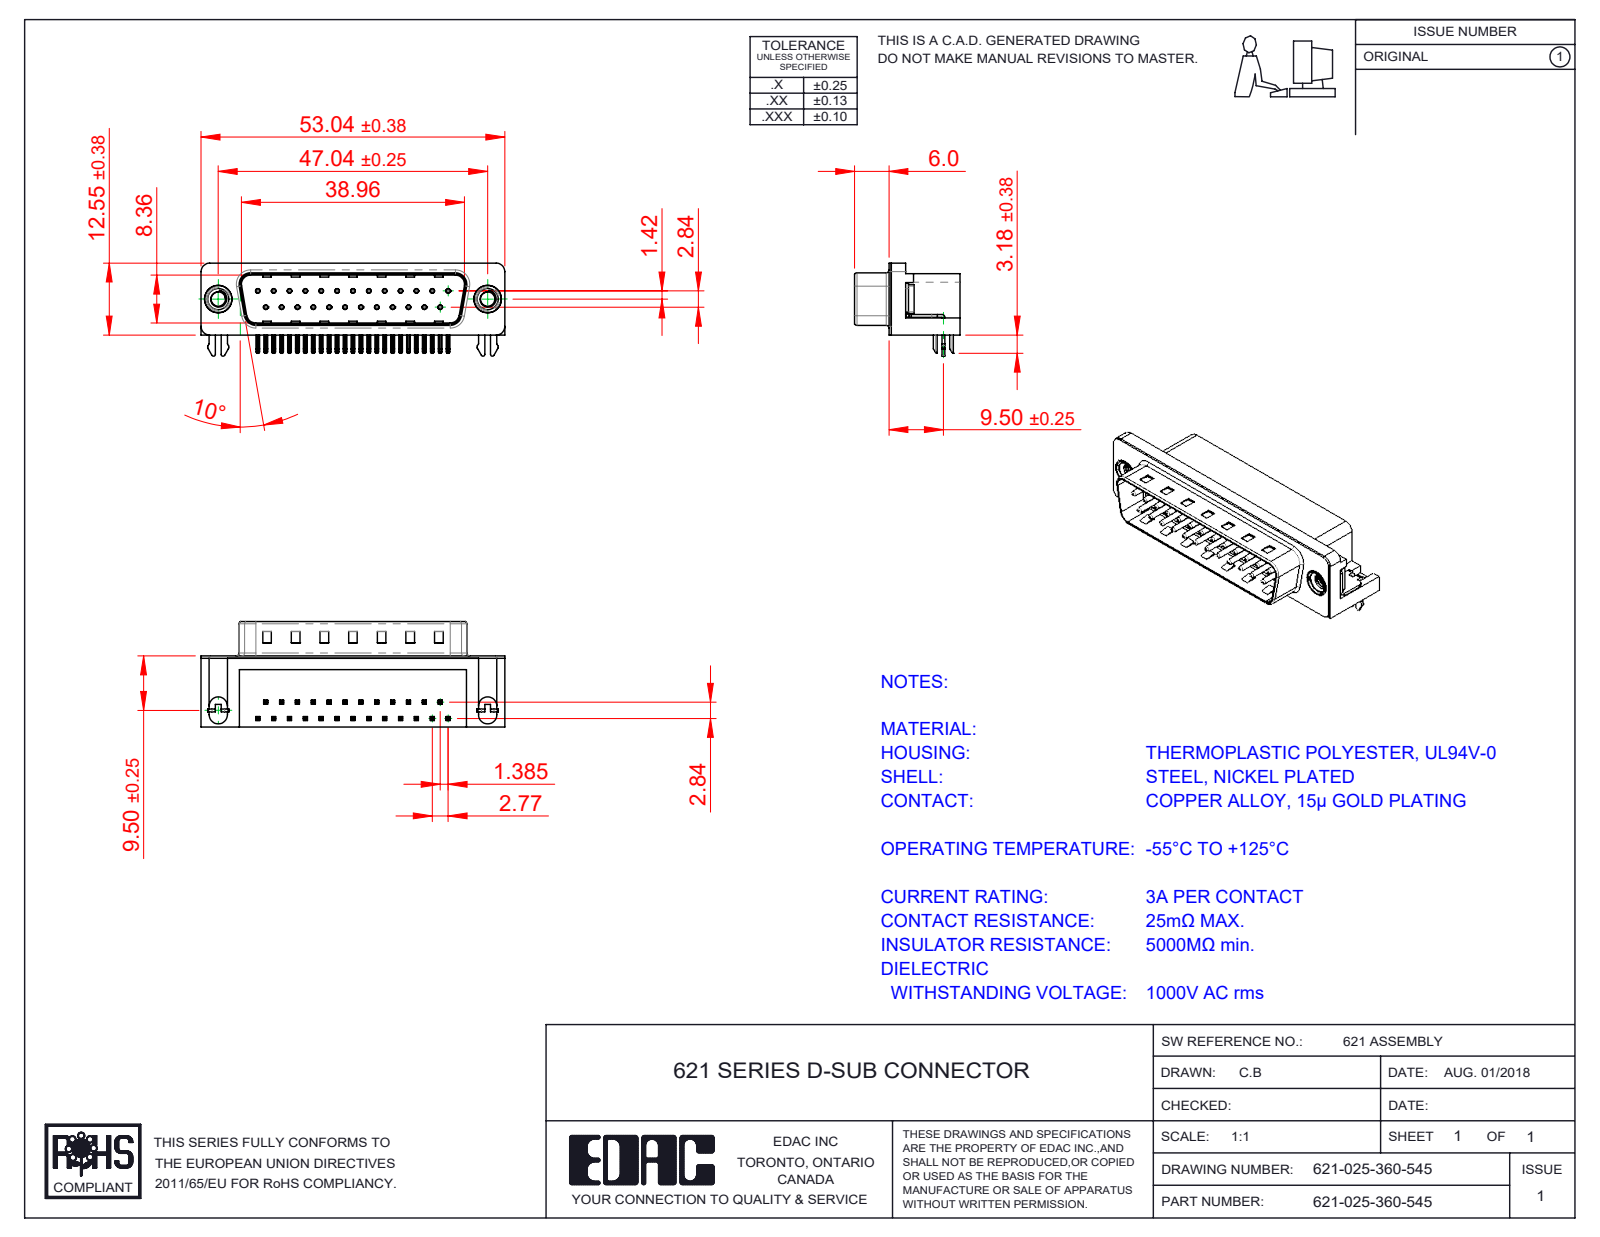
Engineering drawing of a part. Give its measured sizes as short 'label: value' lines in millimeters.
name: 621 Contact Top; 621 M3 Threaded Rivet; 621 Shell_25 Socket; 621 4 Prong Board Lock (+3 more)
written by: SolidWorks 2016 (CONFIG_CONTROL_DESIGN)
unit: mm
bodies: 31 solids, 2383 faces (1447 planar, 669 cylindrical, 267 other)
size: 53.04 × 18.4 × 16.25
volume: 6 352 mm³; area: 7 761 mm²
holes: 25× ⌀0.35, 25× ⌀0.8, 2× ⌀2, 2× ⌀2.5, 2× ⌀4, 2× ⌀4.8, 2× ⌀5
bosses: 25× ⌀0.75, 2× ⌀4.9, 2× ⌀4.75, 2× ⌀3.9, 2× ⌀3
rounds: 112× R0.25, 50× R0.12, 16× R1, 9× R0.5, 8× R1.6, 7× R1.5, 4× R0.9, 4× R2
face distances: 0.4, 12, 10.35, 2.1, 8.76, 10.46, 1.7, 10.86, 12.4, 9
hole spacings: 3.16, 2.77, 5.54, 8.31, 11.08, 13.85, 16.62, 5.03
